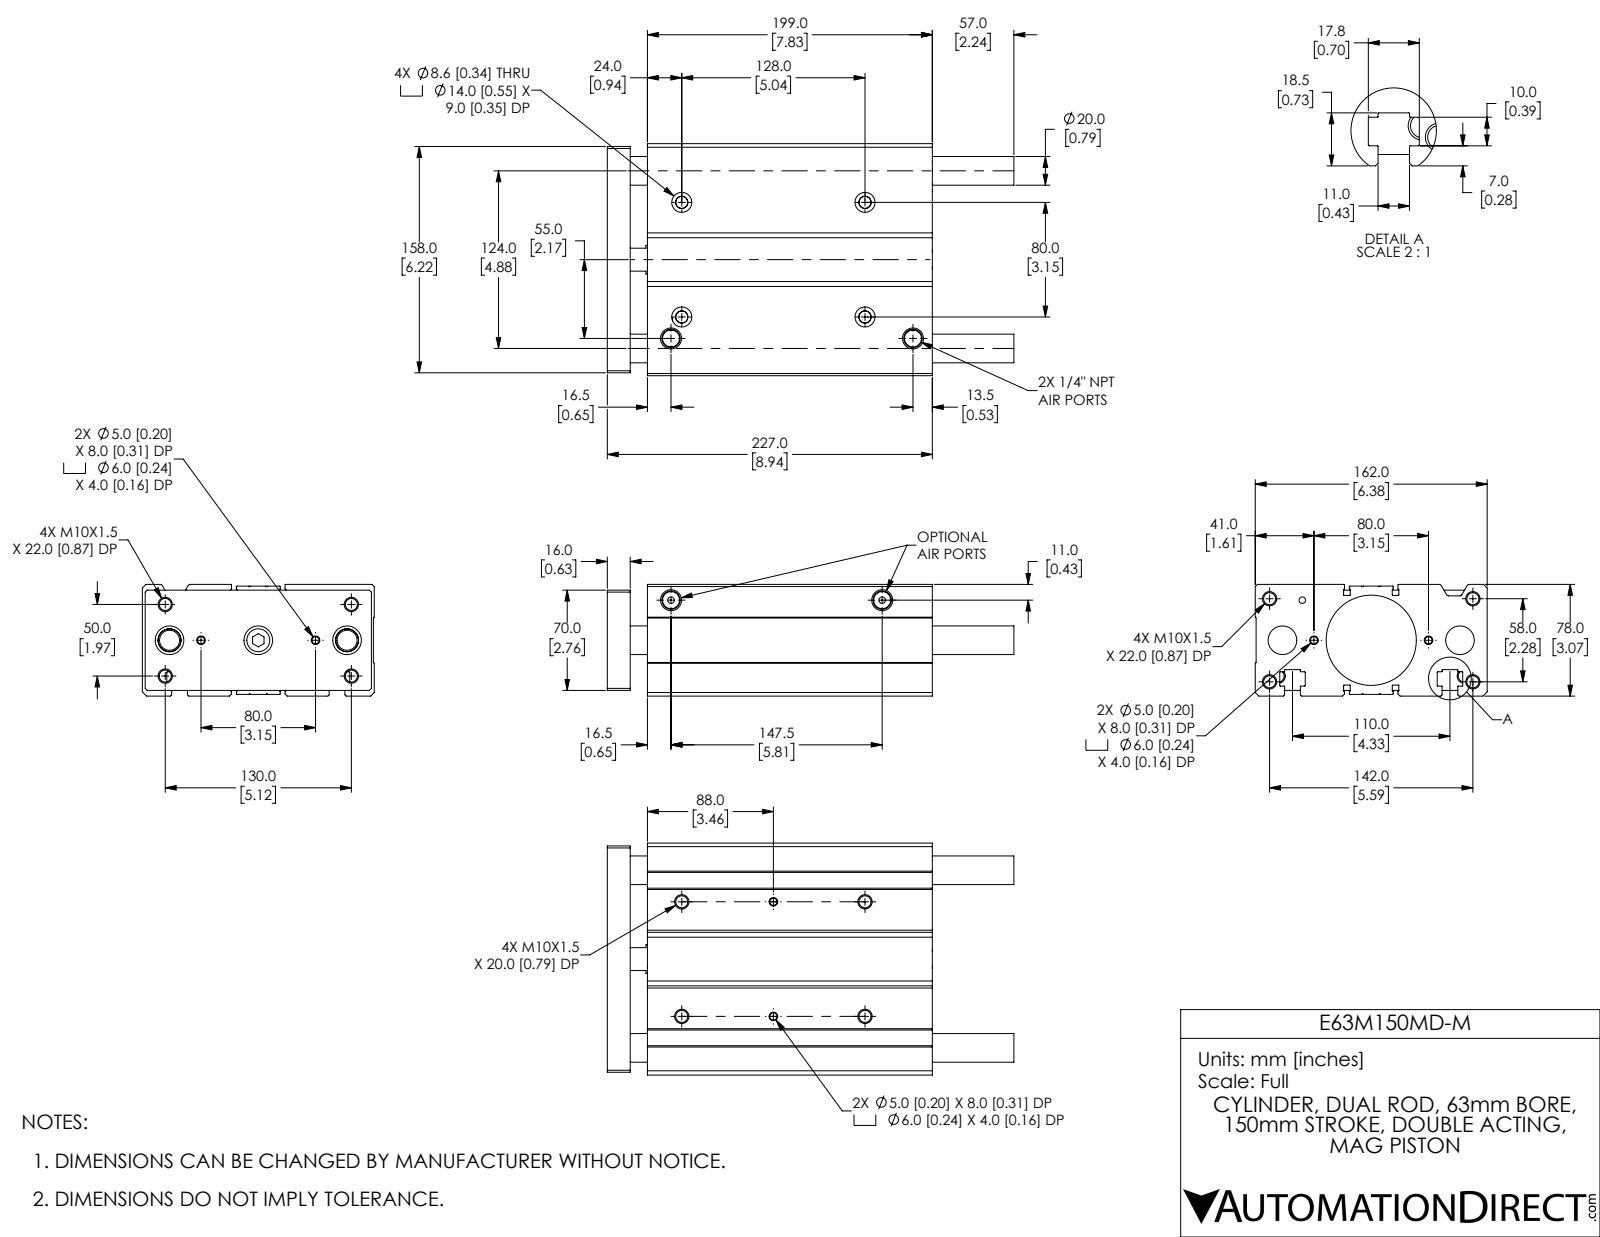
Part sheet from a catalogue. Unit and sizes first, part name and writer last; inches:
Units: inches
Overall size (bounding box): 11.181 × 6.378 × 3.071
Round holes (diameter × count): ⌀0.33 ×12, ⌀0.197 ×4, ⌀0.236 ×4, ⌀0.339 ×4, ⌀0.551 ×4, ⌀0.18 ×3, ⌀0.394 ×3, ⌀0.787 ×3, ⌀0.63 ×2, ⌀0.787 ×1, ⌀2.48 ×1, ⌀2.48 ×1
Round bosses / shafts (diameter × count): ⌀0.63 ×1
Partial cylindrical surfaces — rounded edges, fillets, slot ends (radius × count): R0.008 ×32, R0.016 ×28, R0.059 ×4, R0.012 ×2
Main face-to-face distances: 3.071, 0.047, 3.024, 1.102, 0.63, 0.472, 0.157, 0.024, 6.378, 8.937
Hole centre spacings: 0.284, 0.991, 1.195, 1.392, 1.671, 2.139, 2.52, 2.742
Volume: 127.7 in³ · Surface area: 506.2 in²
Bodies: 5 solids, 421 faces (139 planar, 190 cylindrical, 92 other)
Part name (STEP PRODUCT): E63M150MD-M; E63M150MD-M_BODY; E63M150MD-M_ENDPLATE
STEP written by: SolidWorks 2019 (CONFIG_CONTROL_DESIGN)
